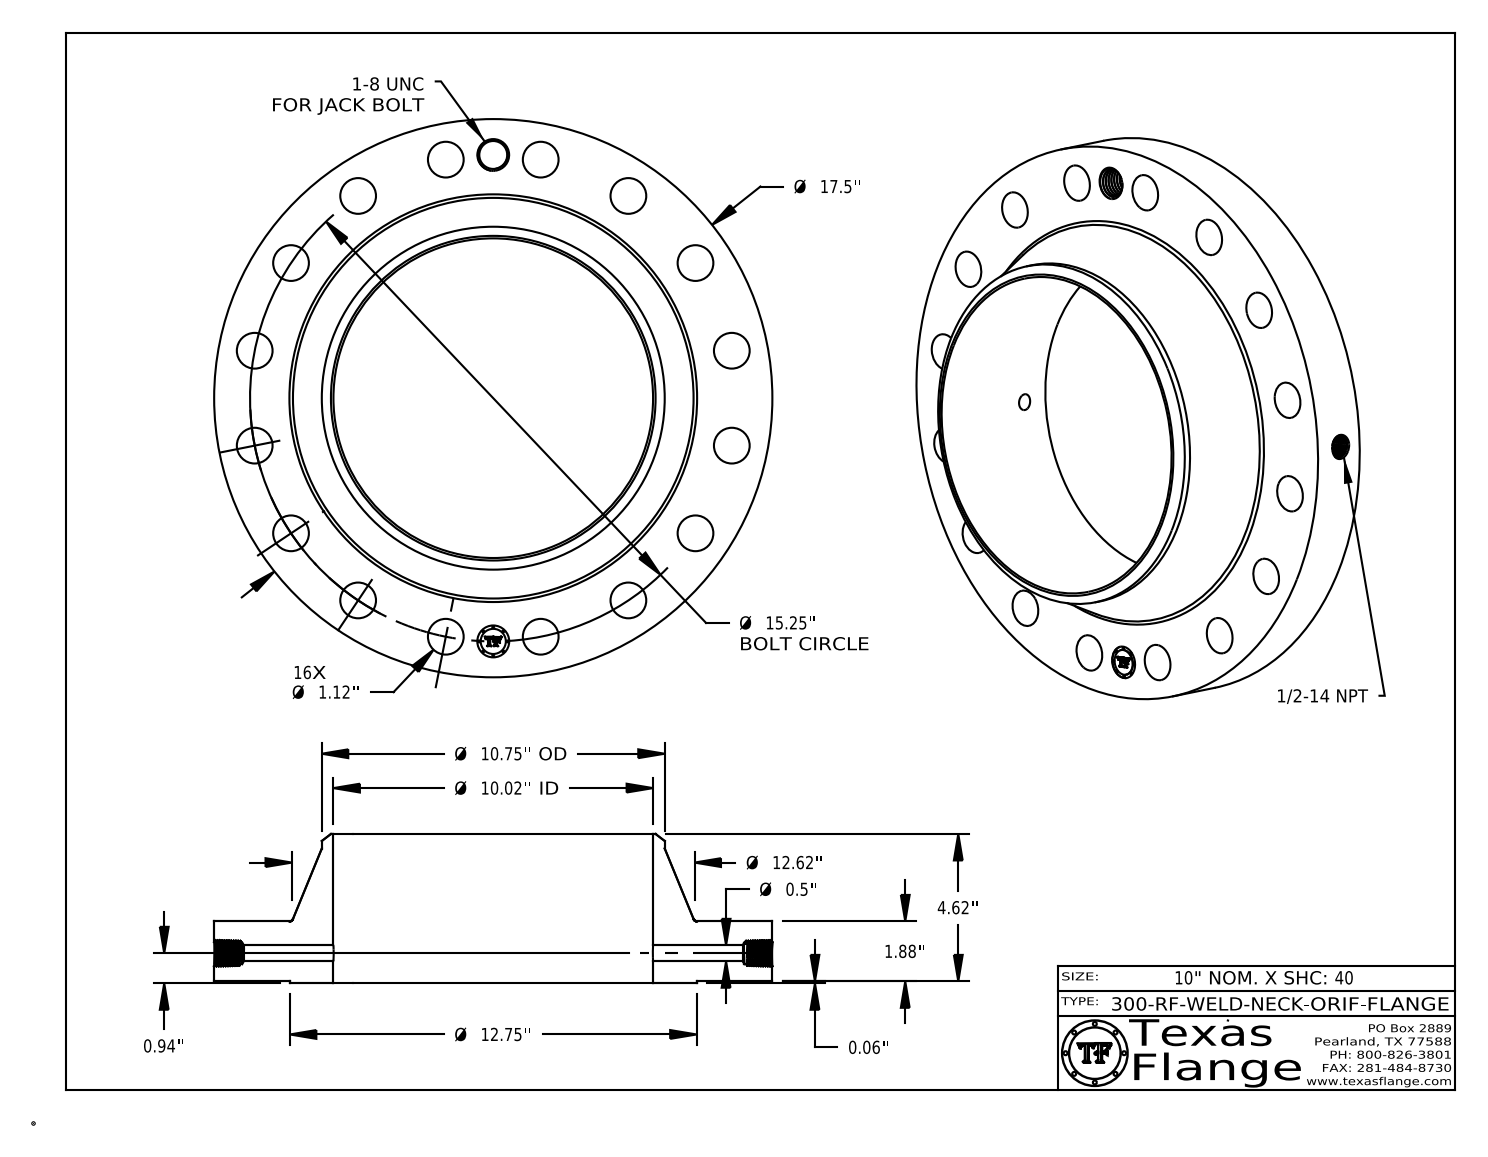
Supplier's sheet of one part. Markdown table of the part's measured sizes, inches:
| quantity | value |
| --- | --- |
| part name | 300-RF-WELD-NECK |
| STEP written by | CATIA V5 STEP AP214 (AUTOMOTIVE_DESIGN) |
| units | inches |
| bodies | 1 solid, 787 faces (369 planar, 109 cylindrical, 309 other) |
| overall size | 17.5 × 17.5 × 4.68 |
| volume | 343.8 in³ |
| surface area | 738.4 in² |
| round holes (diameter × count) | 1.12 × 16, 0.5 × 1, 0.672 × 1, 0.875 × 1, 1 × 1, 10.02 × 1 |
| round bosses / shafts (diameter × count) | 0.061 × 8, 17.5 × 1, 12.75 × 1, 10.75 × 1, 0.788 × 1 |
| main face-to-face distances | 1.88, 0.06, 1.94, 4.68, 4.62, 2.74, 0.015, 1.925, 1.865, 2.755 |
| hole center spacings | 5.836, 7.625, 10.783, 14.089, 14.957, 2.975, 2.975, 8.472 |
